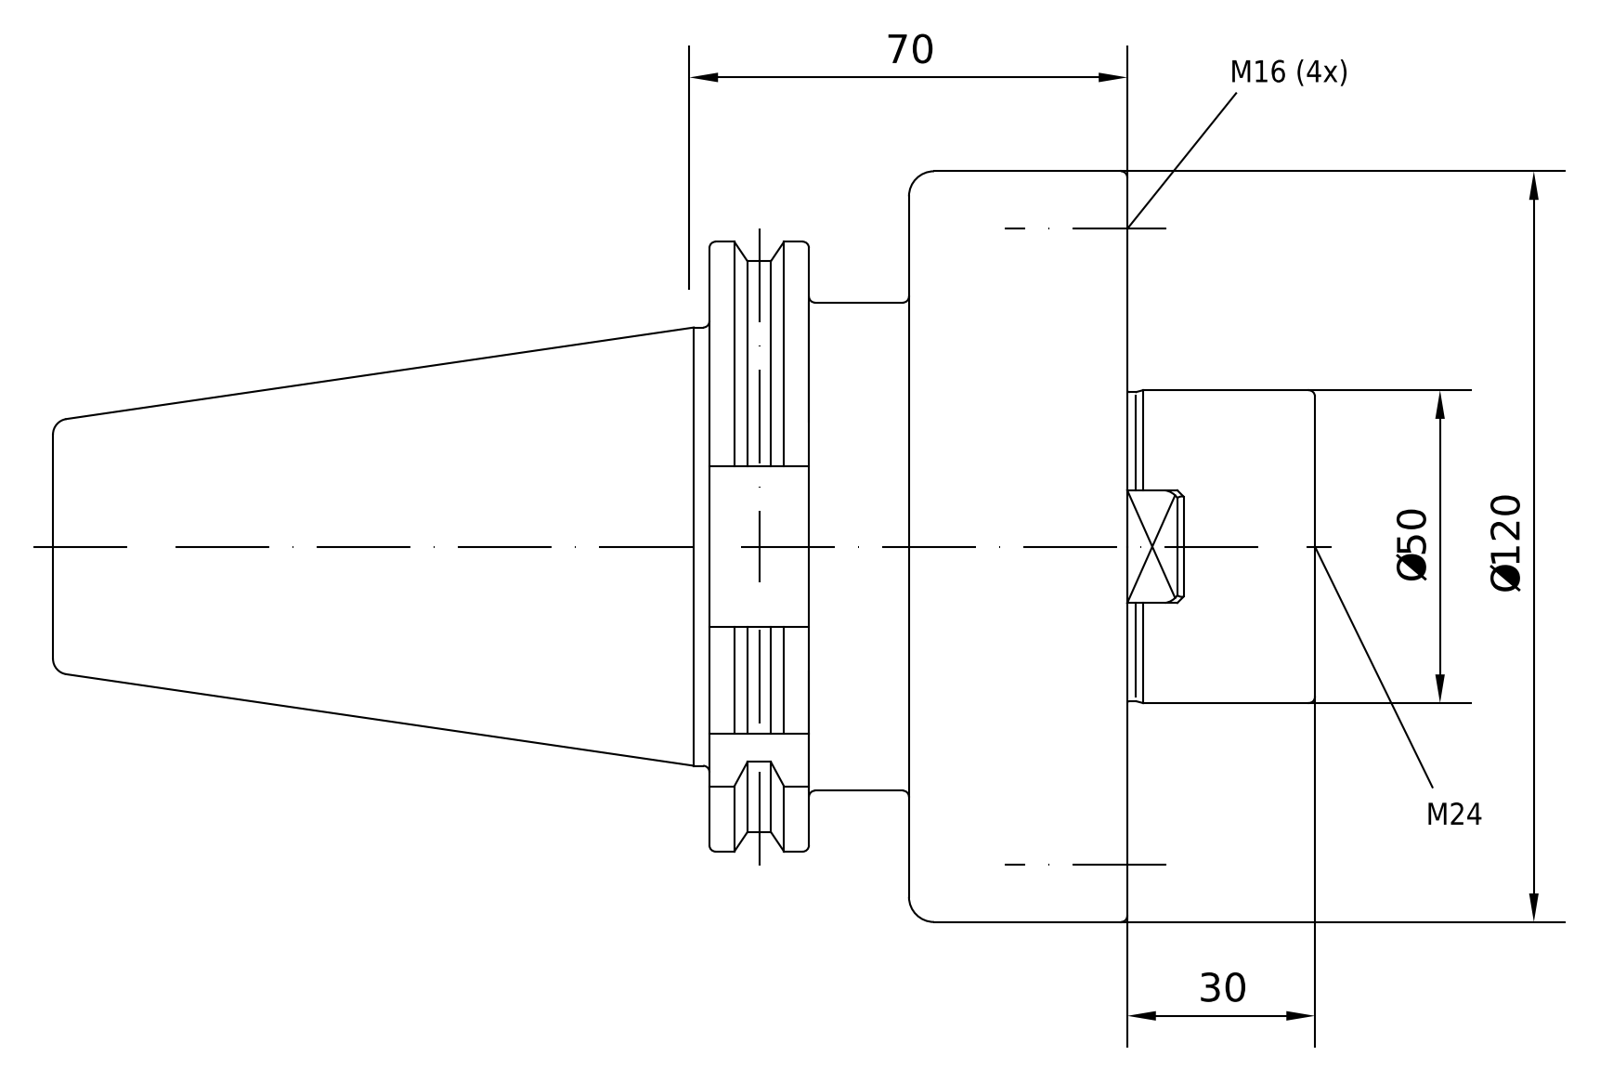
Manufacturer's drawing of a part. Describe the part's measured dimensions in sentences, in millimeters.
The part is named "50-350-50". Its 3-D file was written by "PRO/ENGINEER BY PARAMETRIC TECHNOLOGY CORPORATION, 2010430 (CONFIG_CONTROL_DESIGN)". It is 1 solid with 146 faces: 38 planar, 46 cylindrical and 62 other. Overall it measures 201.6 by 120 by 120 millimeters. Its volume is 832 722 cubic millimeters and its surface area 95 786 square millimeters. Round holes: 4 of diameter 14, 4 of diameter 16, 1 of diameter 20.75, 1 of diameter 21, 1 of diameter 24, 1 of diameter 25.01, 1 of diameter 25.7. Round bosses or shafts: 1 of diameter 120, 1 of diameter 91, 1 of diameter 69.15, 1 of diameter 50, 1 of diameter 24.01. Partial cylindrical surfaces (rounded edges, fillets, slot ends): 1 of radius 1.75, 1 of radius 39, 1 of radius 48.74. The main face-to-face distances are 34.95, 31.85, 66.8, 15.85, 16, 50.95, 96.8, 80.95, 64.95, 30. The hole center spacings are 50.8, 71.84, 101.6.
